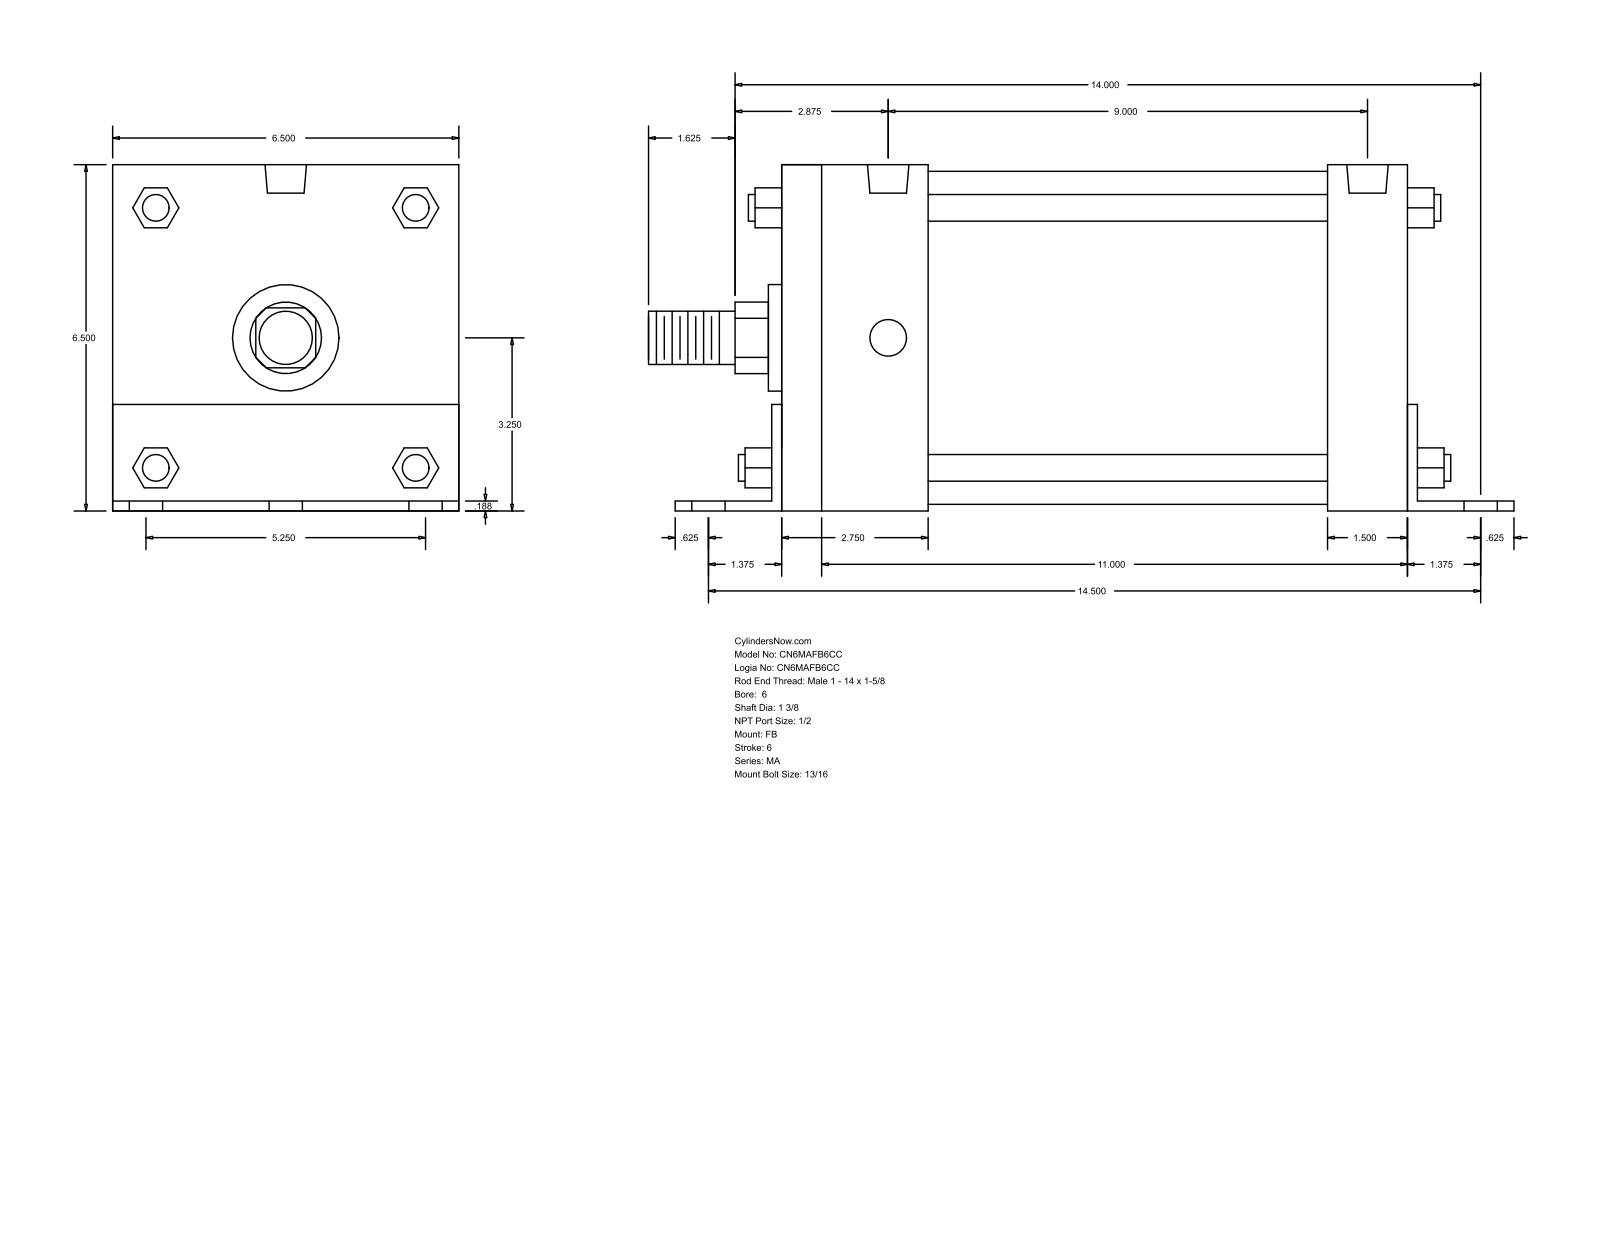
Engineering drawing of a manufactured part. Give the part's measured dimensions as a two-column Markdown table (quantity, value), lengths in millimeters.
| quantity | value |
| --- | --- |
| part name | MA_FB__0600_1.375 |
| STEP written by | GSSL Pune (CONFIG_CONTROL_DESIGN) |
| units | millimeters |
| bodies | 0 solids, 140 faces (105 planar, 35 cylindrical, 0 other) |
| overall size | 409.57 × 165.15 × 165.1 |
| round holes (diameter × count) | 20.64 × 6, 17.46 × 4, 19.77 × 2 |
| round bosses / shafts (diameter × count) | 12.7 × 4, 158.75 × 1, 50.8 × 1, 34.92 × 1, 25.4 × 1 |
| partial cylindrical surfaces (radius × count) | 17.06 × 1, 32.05 × 1 |
| main face-to-face distances | 165.1, 4.76, 295.27, 165.15, 4.71, 160.39, 4.77, 38.1, 42.86, 304.8 |
| hole center spacings | 66.67, 371.17, 365.13, 83.82, 85.78, 108.6, 133.34, 225.42 |
